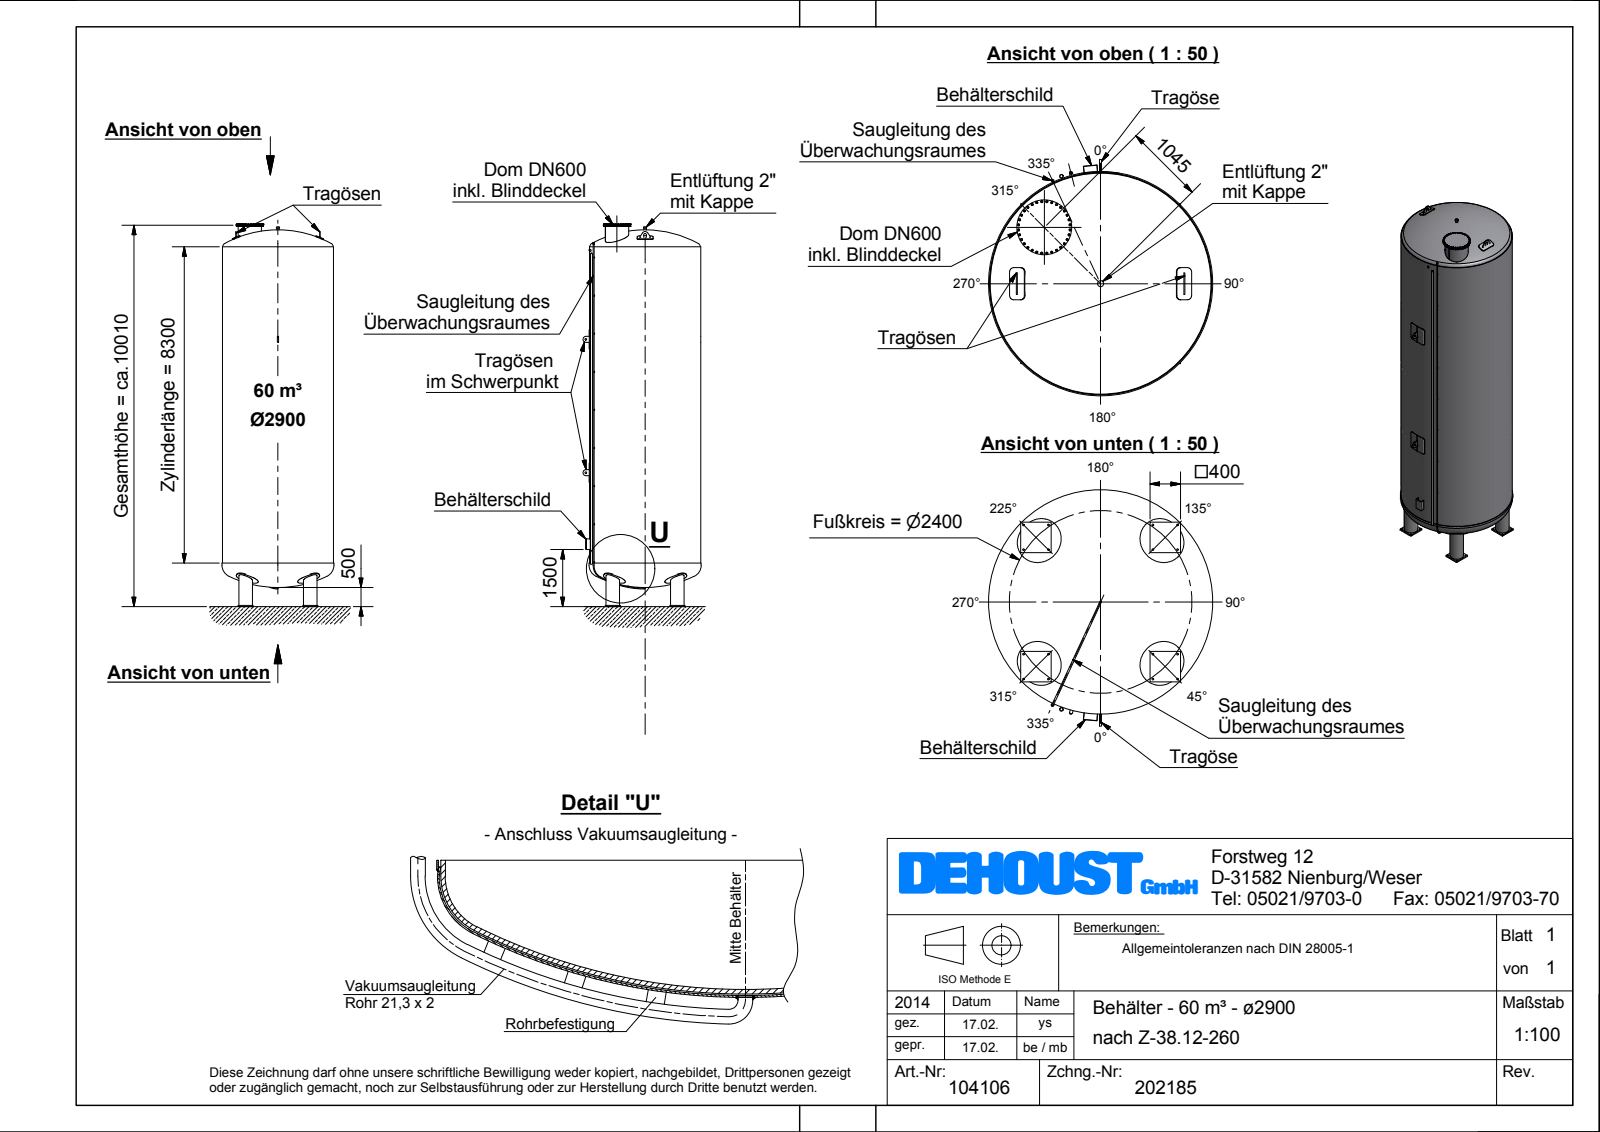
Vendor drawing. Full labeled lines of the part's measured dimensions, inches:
Part name (STEP PRODUCT): Z-38_12-260_Beh\S\dlter_\S\x2900_060m\S\3_Dichte=1,0
STEP written by: Autodesk Inventor 2012 (AUTOMOTIVE_DESIGN)
Units: inches
Bodies: 14 solids, 1245 faces (741 planar, 162 cylindrical, 342 other)
Overall size (bounding box): 395.221 × 122.087 × 115.827
Volume: 3 581 000 in³ · Surface area: 185 500 in²
Round holes (diameter × count): ⌀9.055 ×4, ⌀13.252 ×4, ⌀23.543 ×1
Round bosses / shafts (diameter × count): ⌀0.886 ×32, ⌀0.63 ×32, ⌀23.622 ×4, ⌀14 ×4, ⌀0.839 ×2, ⌀115.827 ×1, ⌀114.882 ×1, ⌀28.346 ×1
Partial cylindrical surfaces — rounded edges, fillets, slot ends (radius × count): R1.969 ×8, R2.205 ×8, R3.15 ×2, R1.378 ×1, R3.346 ×1, R57.835 ×1
Main face-to-face distances: 371.781, 1.181, 370.6, 394.828, 393.646, 23.047, 393.45, 392.269, 21.669, 1.378
Hole centre spacings: 66.813, 62.647, 94.489, 6.102, 88.386
